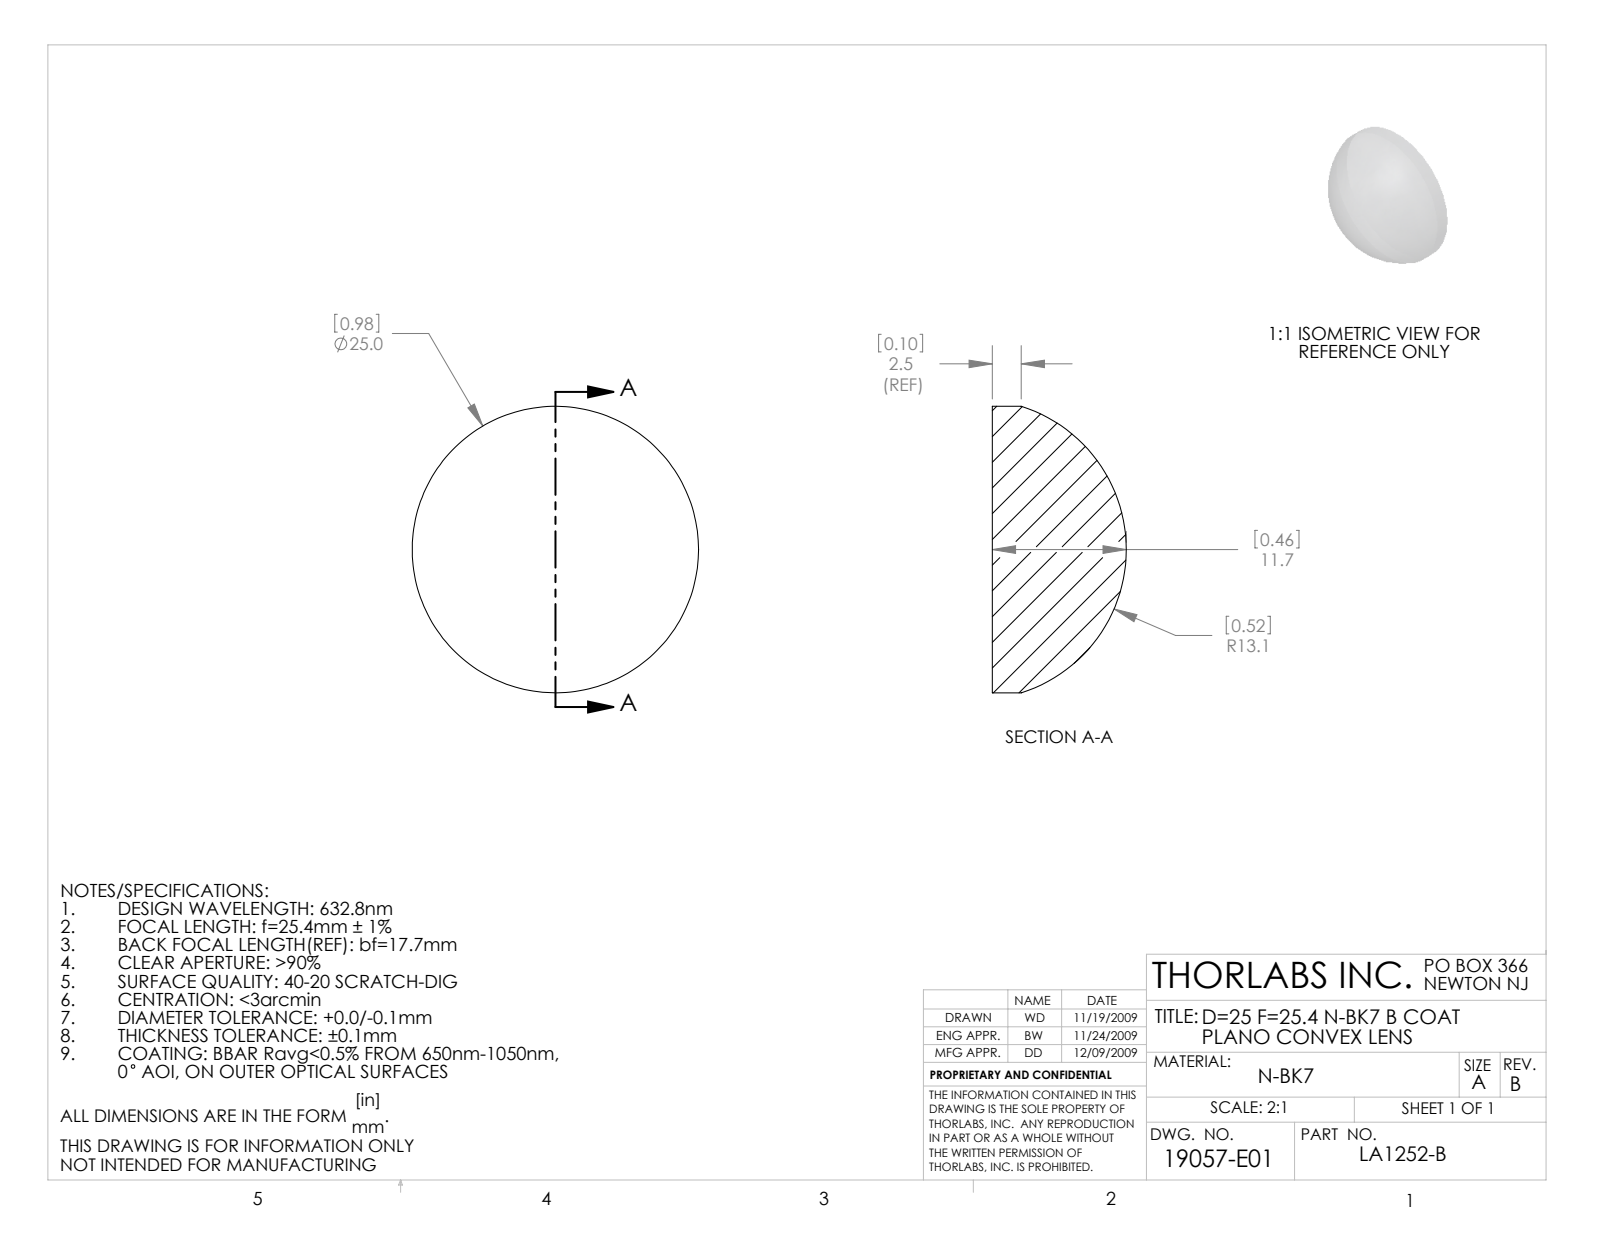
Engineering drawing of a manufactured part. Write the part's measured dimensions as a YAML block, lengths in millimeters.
part_name: "19057-E0W"
step_written_by: "SolidWorks 2009 (AUTOMOTIVE_DESIGN)"
units: millimeters
bodies: {solids: 1, faces: 5, planar: 1, cylindrical: 2, other: 2}
overall_size: [25, 25, 11.7]
volume: 3895
surface_area: 1444
round_bosses_or_shafts:
  - {diameter: 25, count: 1}
